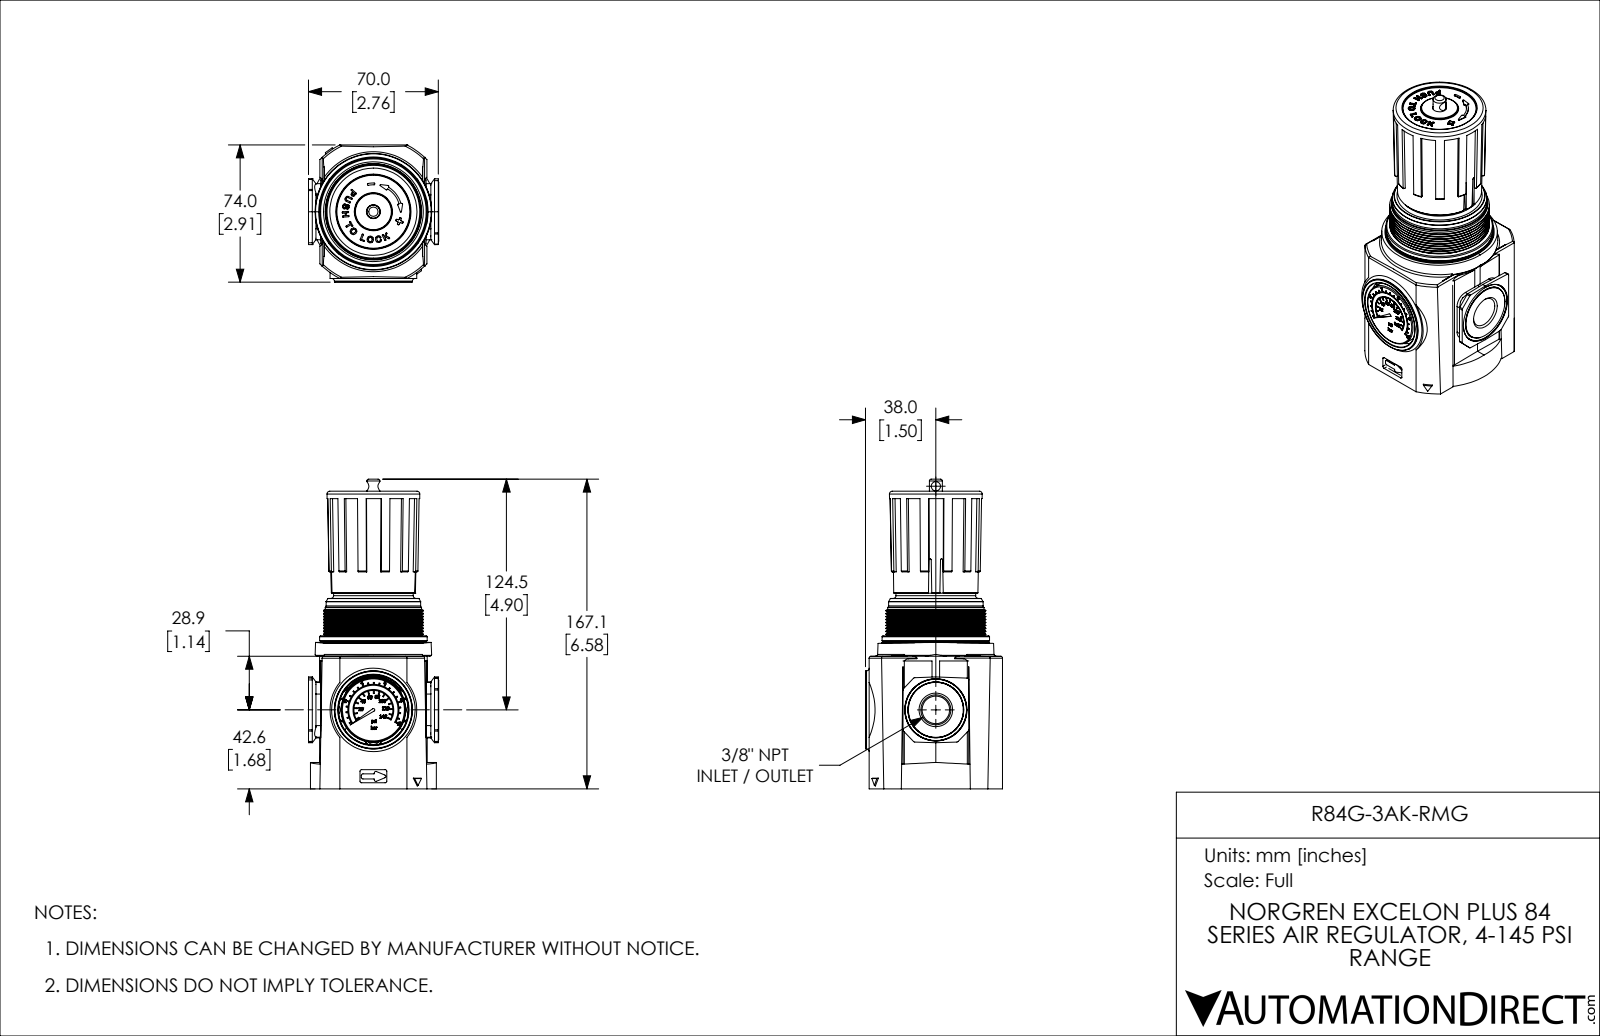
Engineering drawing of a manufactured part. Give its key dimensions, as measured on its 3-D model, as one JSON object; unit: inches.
{"part_name": "R84G-3AK-RMG", "step_written_by": "SolidWorks 2021 (CONFIG_CONTROL_DESIGN)", "units": "inches", "bodies": {"solids": 6, "faces": 2246, "planar": 789, "cylindrical": 1065, "other": 392}, "overall_size": [6.577, 2.913, 2.766], "volume_in3": 28.51, "surface_area_in2": 173.4, "round_holes": [[0.177, 2], [0.059, 1], [0.197, 1], [0.222, 1], [1.319, 1], [2.323, 1]], "round_bosses_or_shafts": [[0.299, 2], [0.157, 2], [2.283, 1], [2.119, 1], [2.047, 1], [2.026, 1], [2.008, 1], [1.732, 1]], "partial_cylinders_radius": [[0.028, 48], [0.012, 27], [0.039, 26], [0.047, 18], [0.03, 16], [0.02, 15], [0.004, 14], [0.06, 12]], "face_to_face_distances": [2.638, 2.035, 0.602, 0.472, 2.508, 3.11, 4.156, 0.512, 3.683, 1.648], "hole_center_spacings": [0.856, 1.713]}
